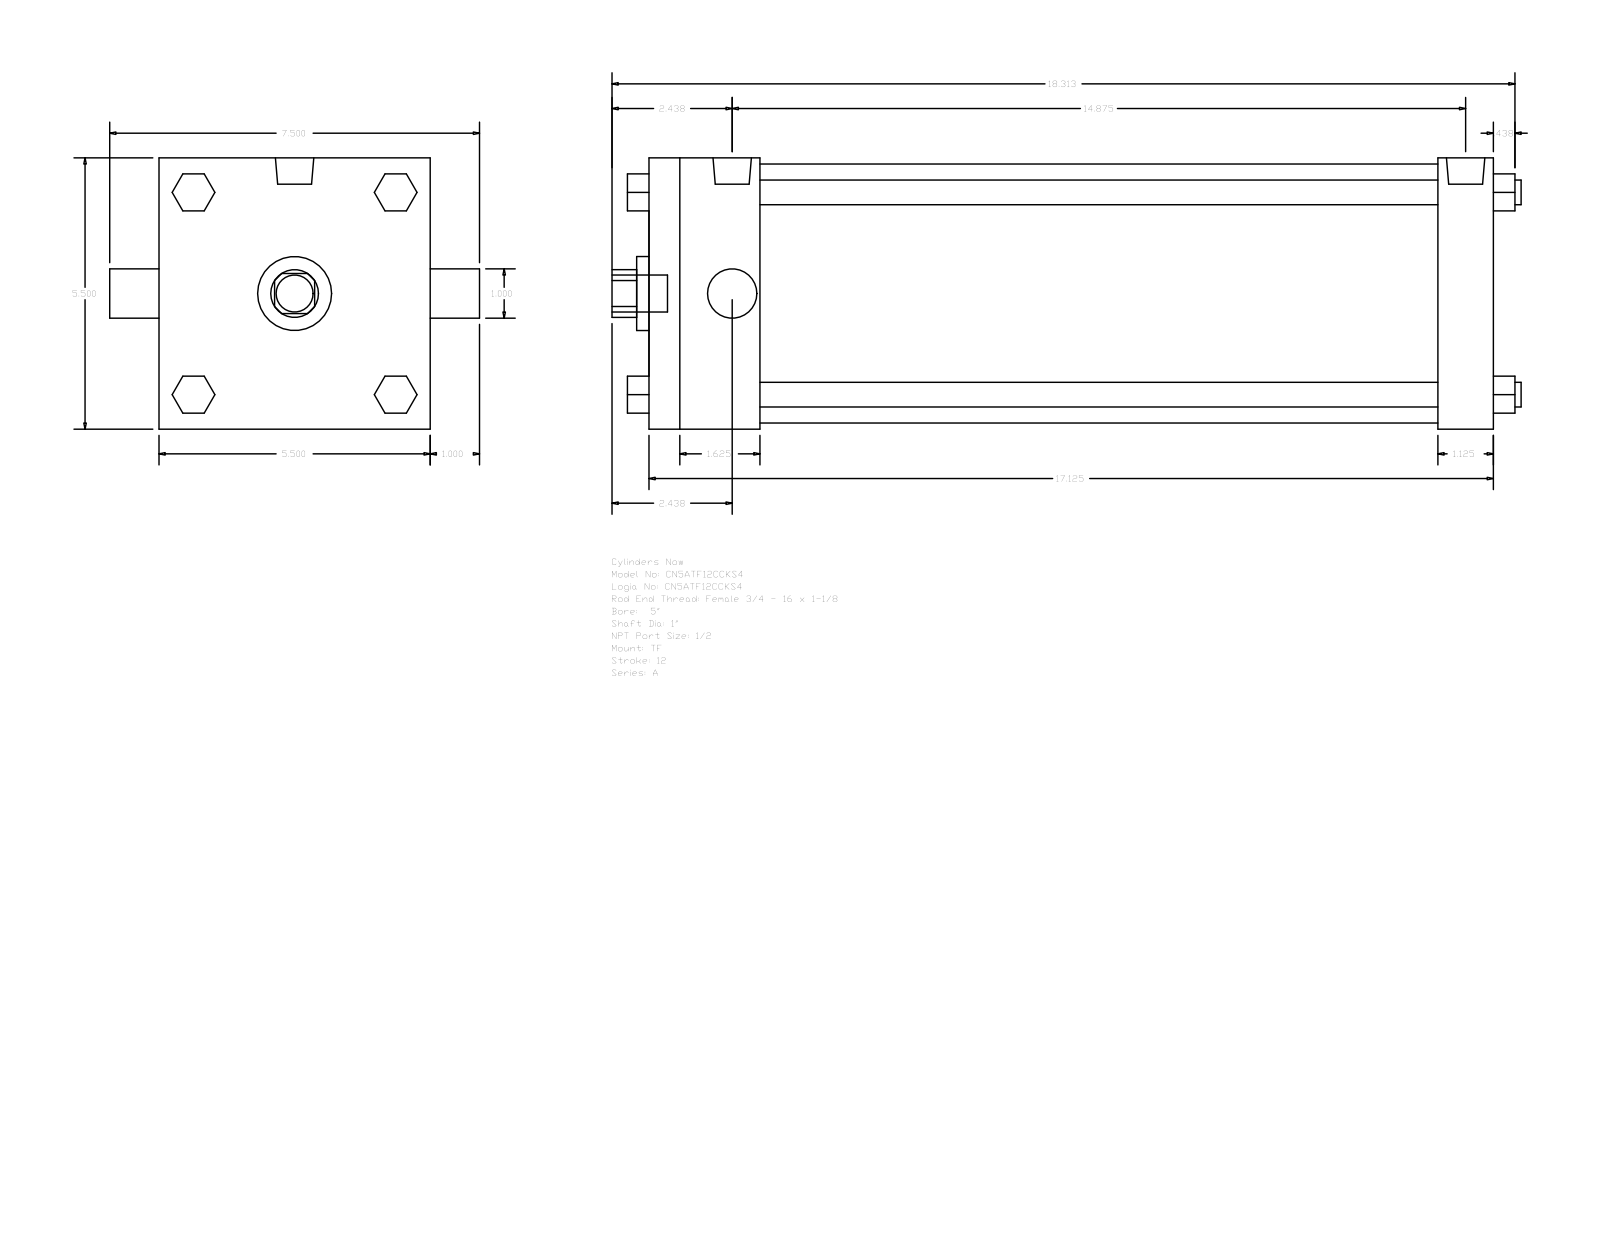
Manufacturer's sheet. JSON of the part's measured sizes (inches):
{"part_name": "A_TF__0500_1", "step_written_by": "GSSL Pune (CONFIG_CONTROL_DESIGN)", "units": "inches", "bodies": {"solids": 0, "faces": 120, "planar": 92, "cylindrical": 28, "other": 0}, "overall_size": [18.437, 7.5, 5.5], "round_holes": [[1, 2], [1.5, 1], [5.25, 1]], "round_bosses_or_shafts": [[0.5, 4], [0.344, 3], [0.778, 2], [0.75, 1]], "partial_cylinders_radius": [[0.484, 1]], "face_to_face_distances": [5.5, 17.125, 1.125, 16, 2.25, 13.75, 14.875, 0.75, 2.05, 3.55]}
